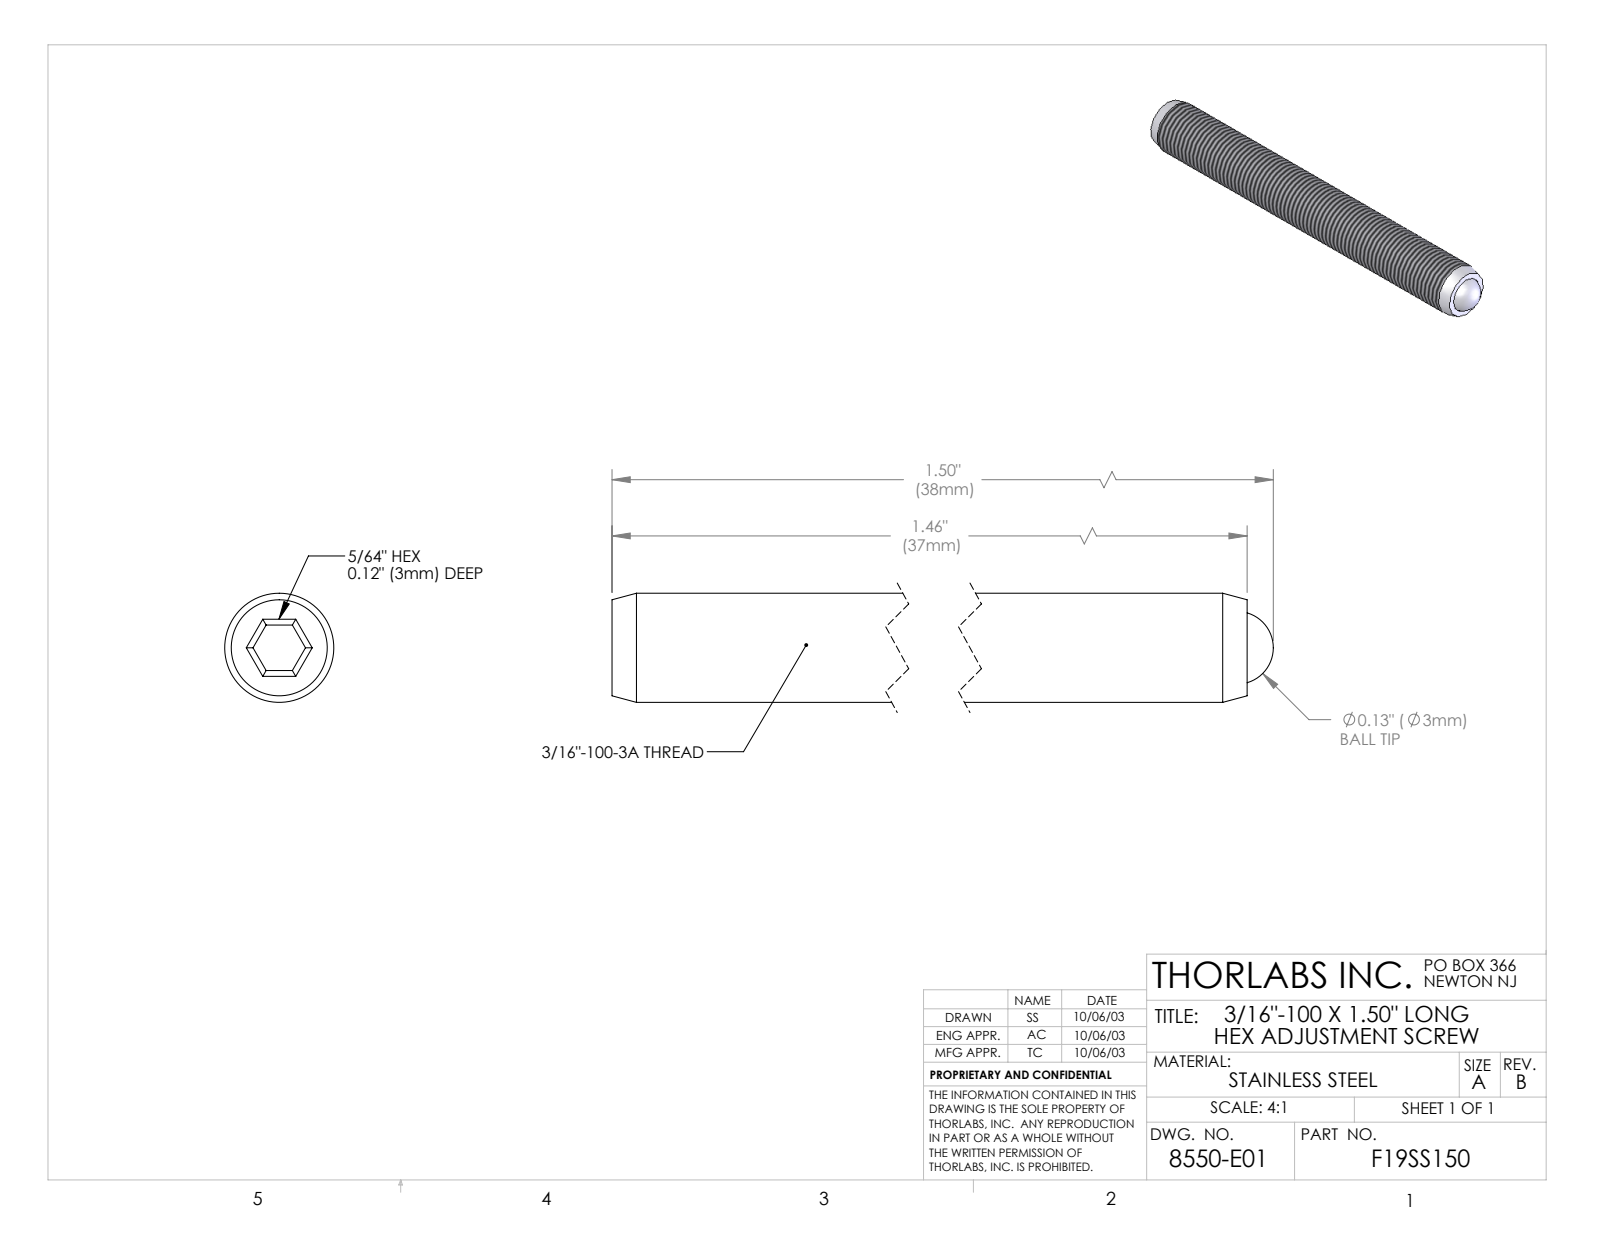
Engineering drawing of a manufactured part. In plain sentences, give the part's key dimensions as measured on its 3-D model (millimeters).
The part is named "8550-E0W". Its 3-D file was written by "SolidWorks 2018 (AUTOMOTIVE_DESIGN)". It is 2 solids with 29 faces: 15 planar, 4 cylindrical and 10 other. Overall it measures 38.1 by 4.76 by 4.76 millimeters. Its volume is 647 cubic millimeters and its surface area 646 square millimeters. Round holes: 1 of diameter 3.19. Round bosses or shafts: 1 of diameter 4.76. The main face-to-face distances are 1.98, 36.96, 3.05, 33.91.
